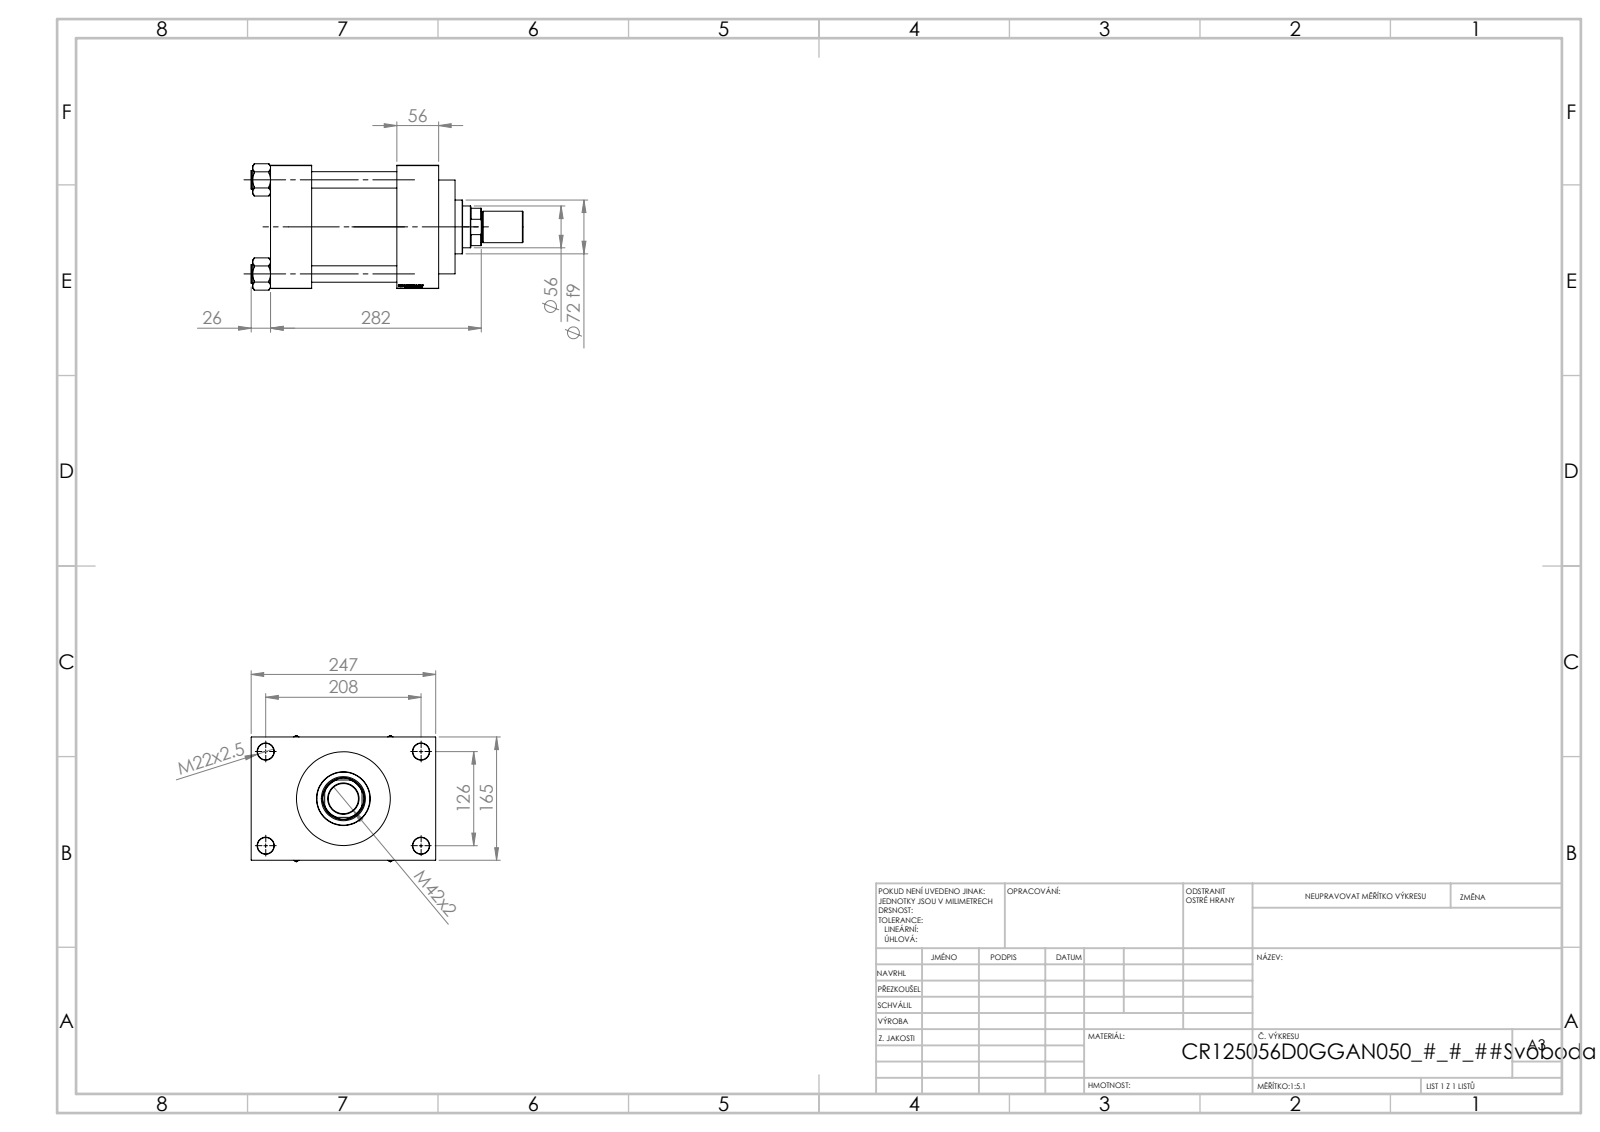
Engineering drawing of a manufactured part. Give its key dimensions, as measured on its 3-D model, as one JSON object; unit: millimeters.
{"part_name": "V215CR_D_TYCINKA; V215CR_D_Body; ROD_END_AH; V215_VC_A (+2 more)", "step_written_by": "SolidWorks 2019 (CONFIG_CONTROL_DESIGN)", "units": "millimeters", "bodies": {"solids": 12, "faces": 1163, "planar": 548, "cylindrical": 91, "other": 524}, "overall_size": [364, 247, 169.14], "volume_mm3": 5191000, "surface_area_mm2": 577892, "round_holes": [[22, 8], [7, 2], [32.24, 2], [45, 2], [40.5, 1], [56, 1], [59, 1], [96, 1], [125, 1], [125.5, 1]], "round_bosses_or_shafts": [[25, 4], [131, 1], [72, 1], [42, 1], [40, 1]], "partial_cylinders_radius": [[27, 1]], "face_to_face_distances": [169, 114, 165, 55, 56, 225, 170, 41, 206, 247], "hole_center_spacings": [41.05, 89.02, 121.59, 125.9, 132.47, 166.95, 209.13, 126]}
